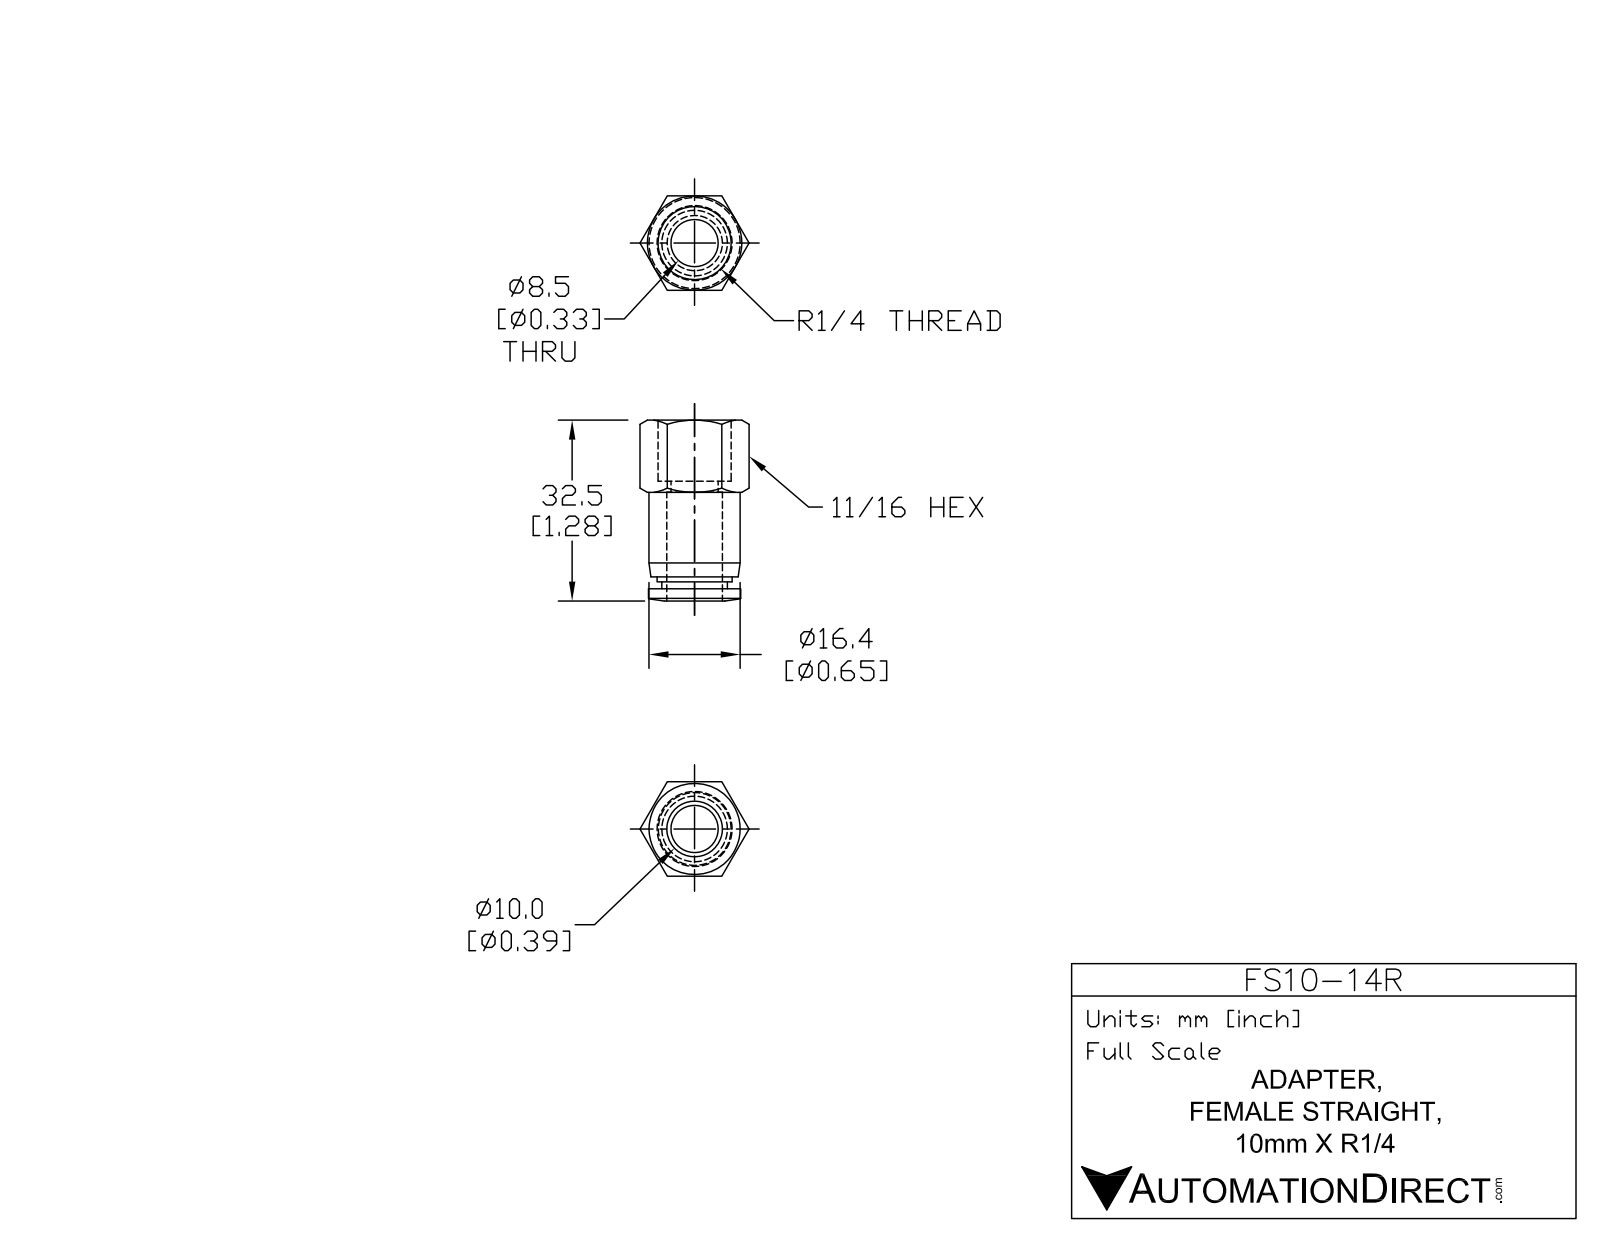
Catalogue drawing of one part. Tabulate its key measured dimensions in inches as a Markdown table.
| quantity | value |
| --- | --- |
| part name | FS10M-14R |
| STEP written by | SolidWorks 2015 (AUTOMOTIVE_DESIGN) |
| units | inches |
| bodies | 1 solid, 50 faces (14 planar, 12 cylindrical, 24 other) |
| overall size | 1.281 × 0.773 × 0.669 |
| volume | 0.243 in³ |
| surface area | 5.265 in² |
| round holes (diameter × count) | 0.335 × 1, 0.406 × 1 |
| round bosses / shafts (diameter × count) | 0.654 × 1, 0.646 × 1, 0.531 × 1, 0.465 × 1 |
| main face-to-face distances | 0.669, 1.195, 0.433, 0.762, 1.11, 0.677, 0.085, 1.146, 0.713, 0.035 |
